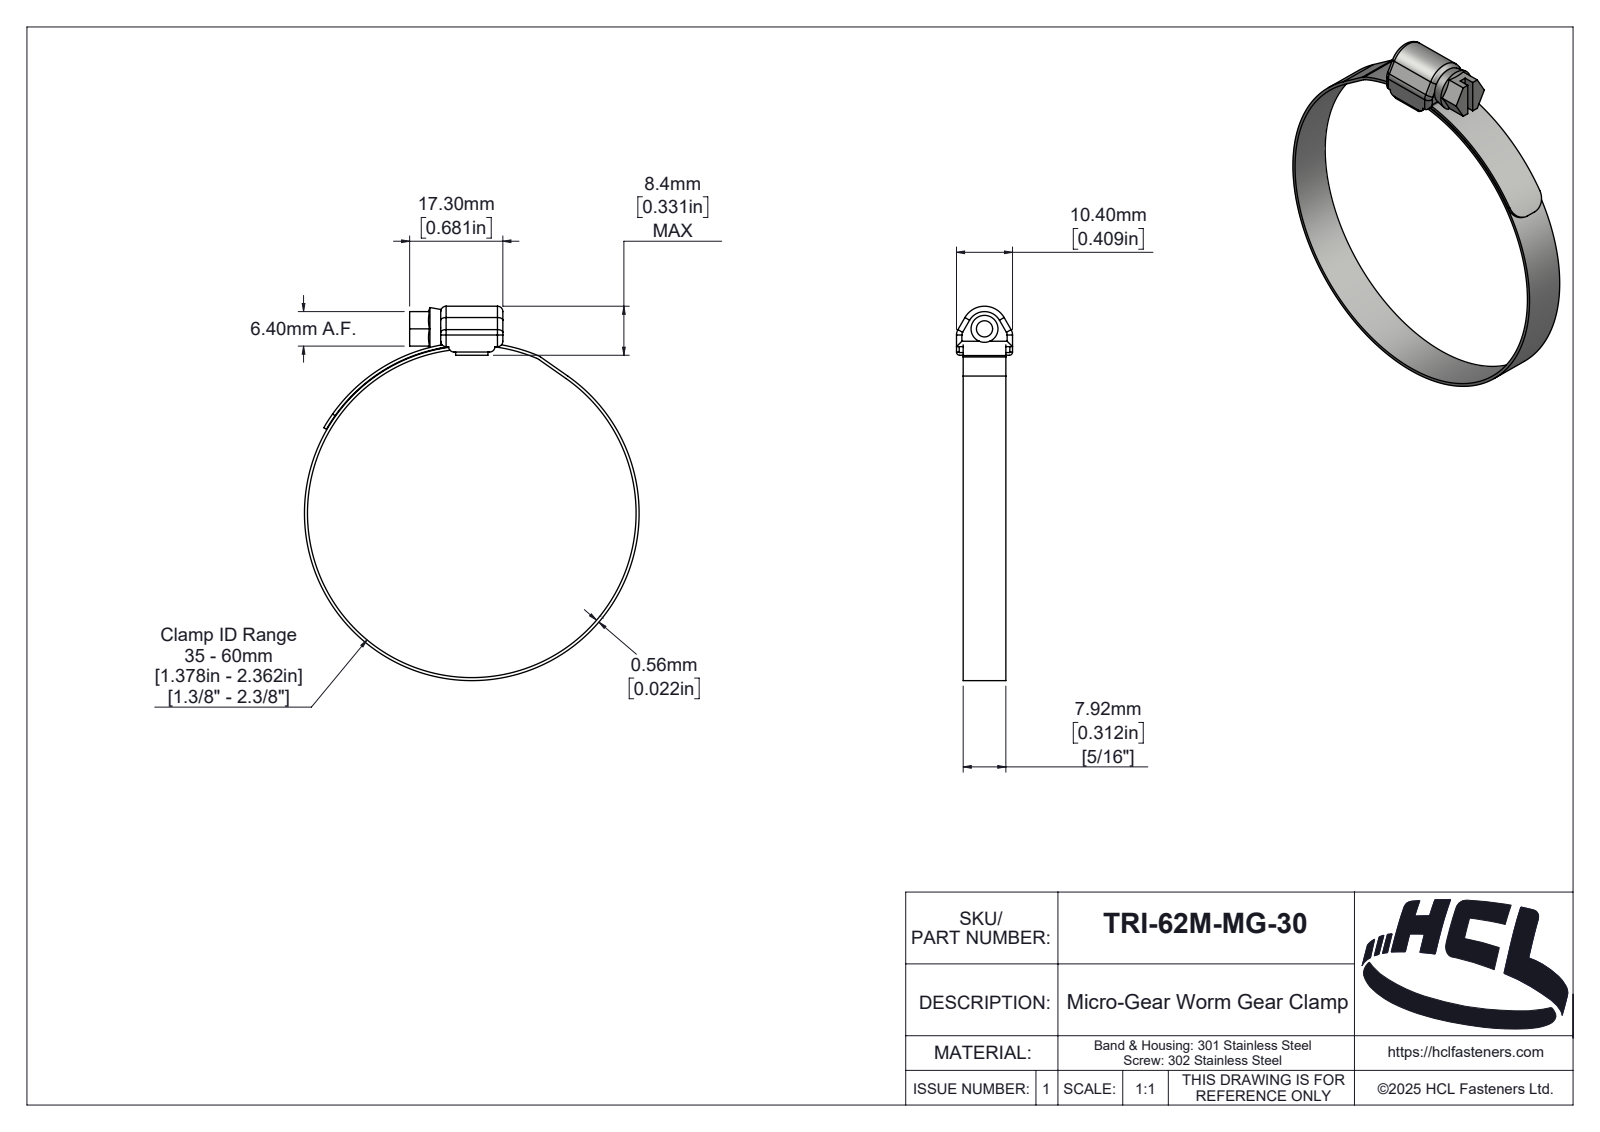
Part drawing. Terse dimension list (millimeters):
name: TRI-62M-MG-30
written by: SolidWorks 2025 (AUTOMOTIVE_DESIGN)
unit: mm
bodies: 3 solids, 186 faces (38 planar, 87 cylindrical, 61 other)
size: 69.46 × 62.12 × 10.4
volume: 1 946 mm³; area: 5 010 mm²
holes: 1× ⌀5, 1× ⌀61
bosses: 1× ⌀62.12
rounds: 12× R1, 3× R2, 2× R0.1, 2× R0.6, 2× R3, 1× R0.25, 1× R1.01, 1× R1.26
face distances: 7.92, 1.1, 0.5, 1.24, 9.16, 1.6, 0.56, 6.2, 10.4, 5.76
